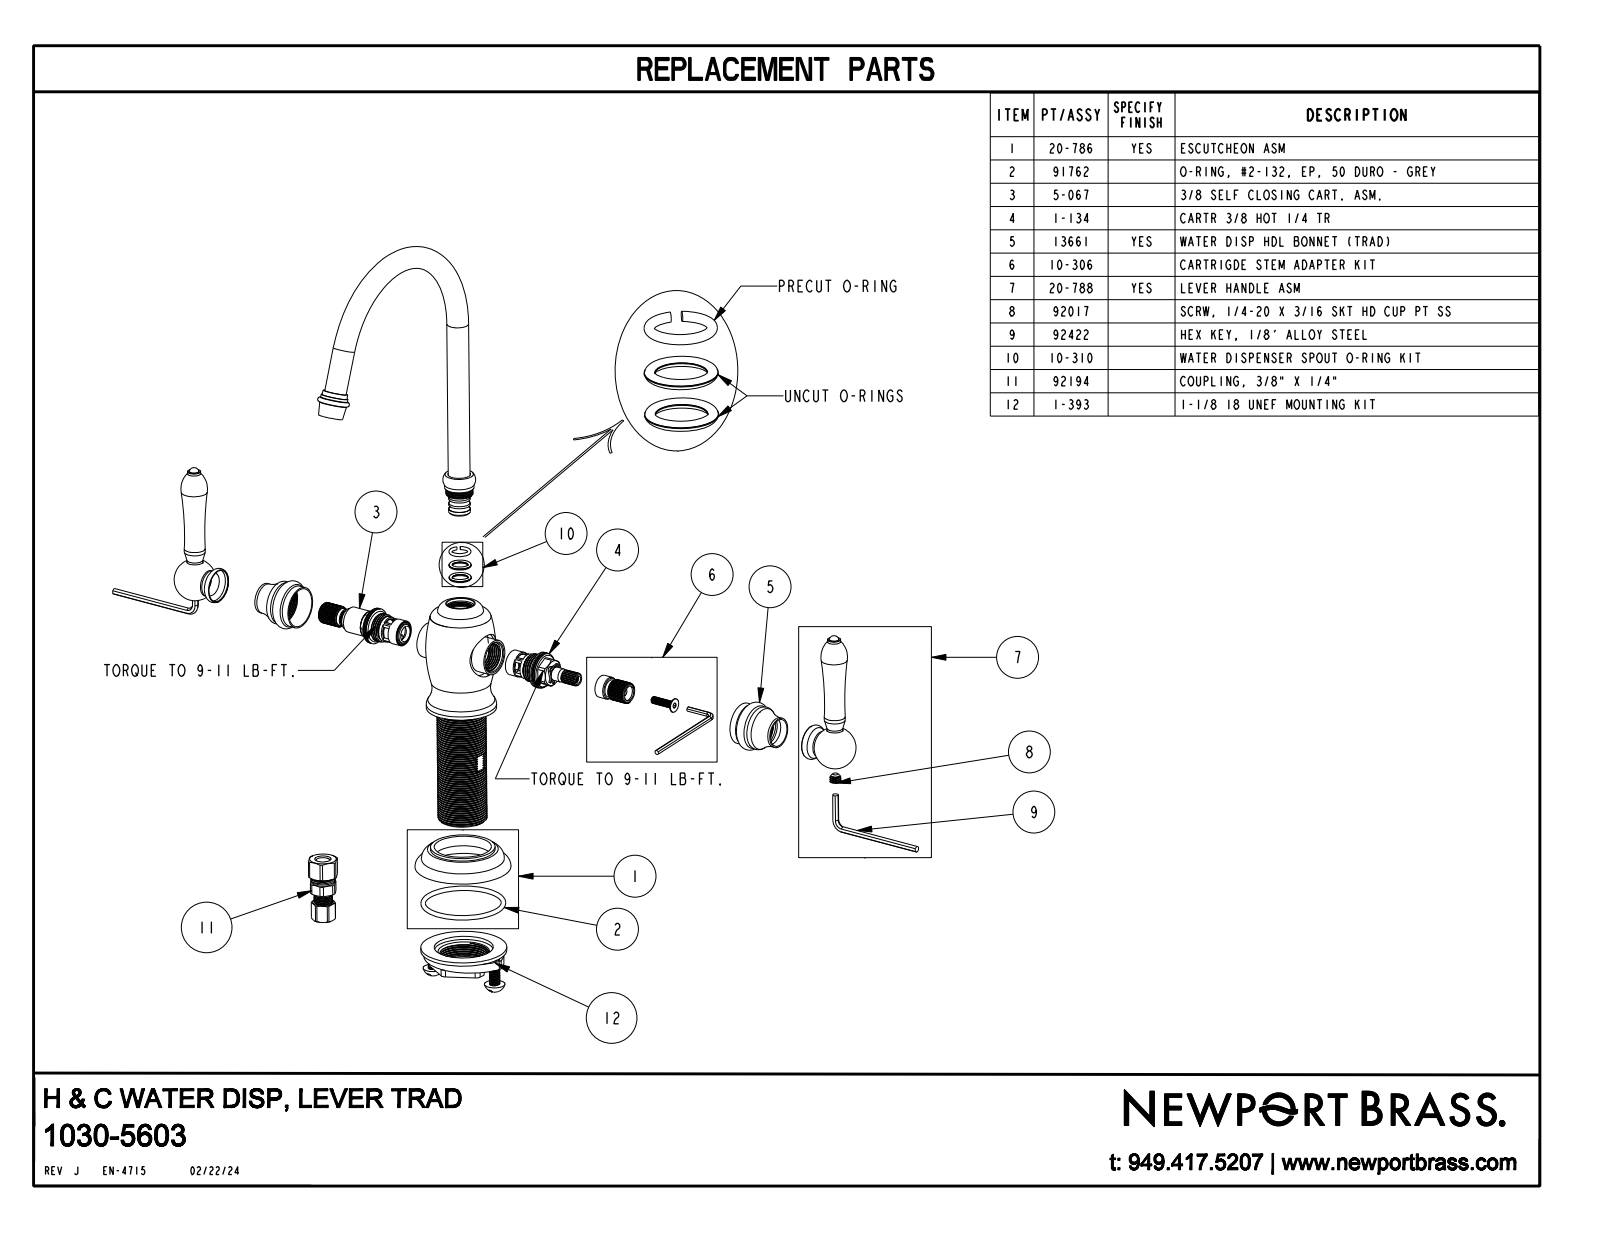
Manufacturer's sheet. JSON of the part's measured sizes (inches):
{"part_name": "1030-5603", "step_written_by": "CREO PARAMETRIC BY PTC INC, 2018400 (CONFIG_CONTROL_DESIGN)", "units": "inches", "bodies": {"solids": 1, "faces": 124, "planar": 14, "cylindrical": 38, "other": 72}, "overall_size": [9.507, 6.182, 5.436], "volume_in3": 11.04, "surface_area_in2": 58.72, "round_holes": [[1, 1]], "round_bosses_or_shafts": [[0.3, 3], [0.5, 2], [0.48, 2], [0.36, 2], [1.61, 1], [0.95, 1], [0.675, 1], [0.625, 1]], "face_to_face_distances": [0.02, 3.23, 3.25, 3.21, 1.02, 2.23, 1, 2.21, 3.307, 1.21]}
